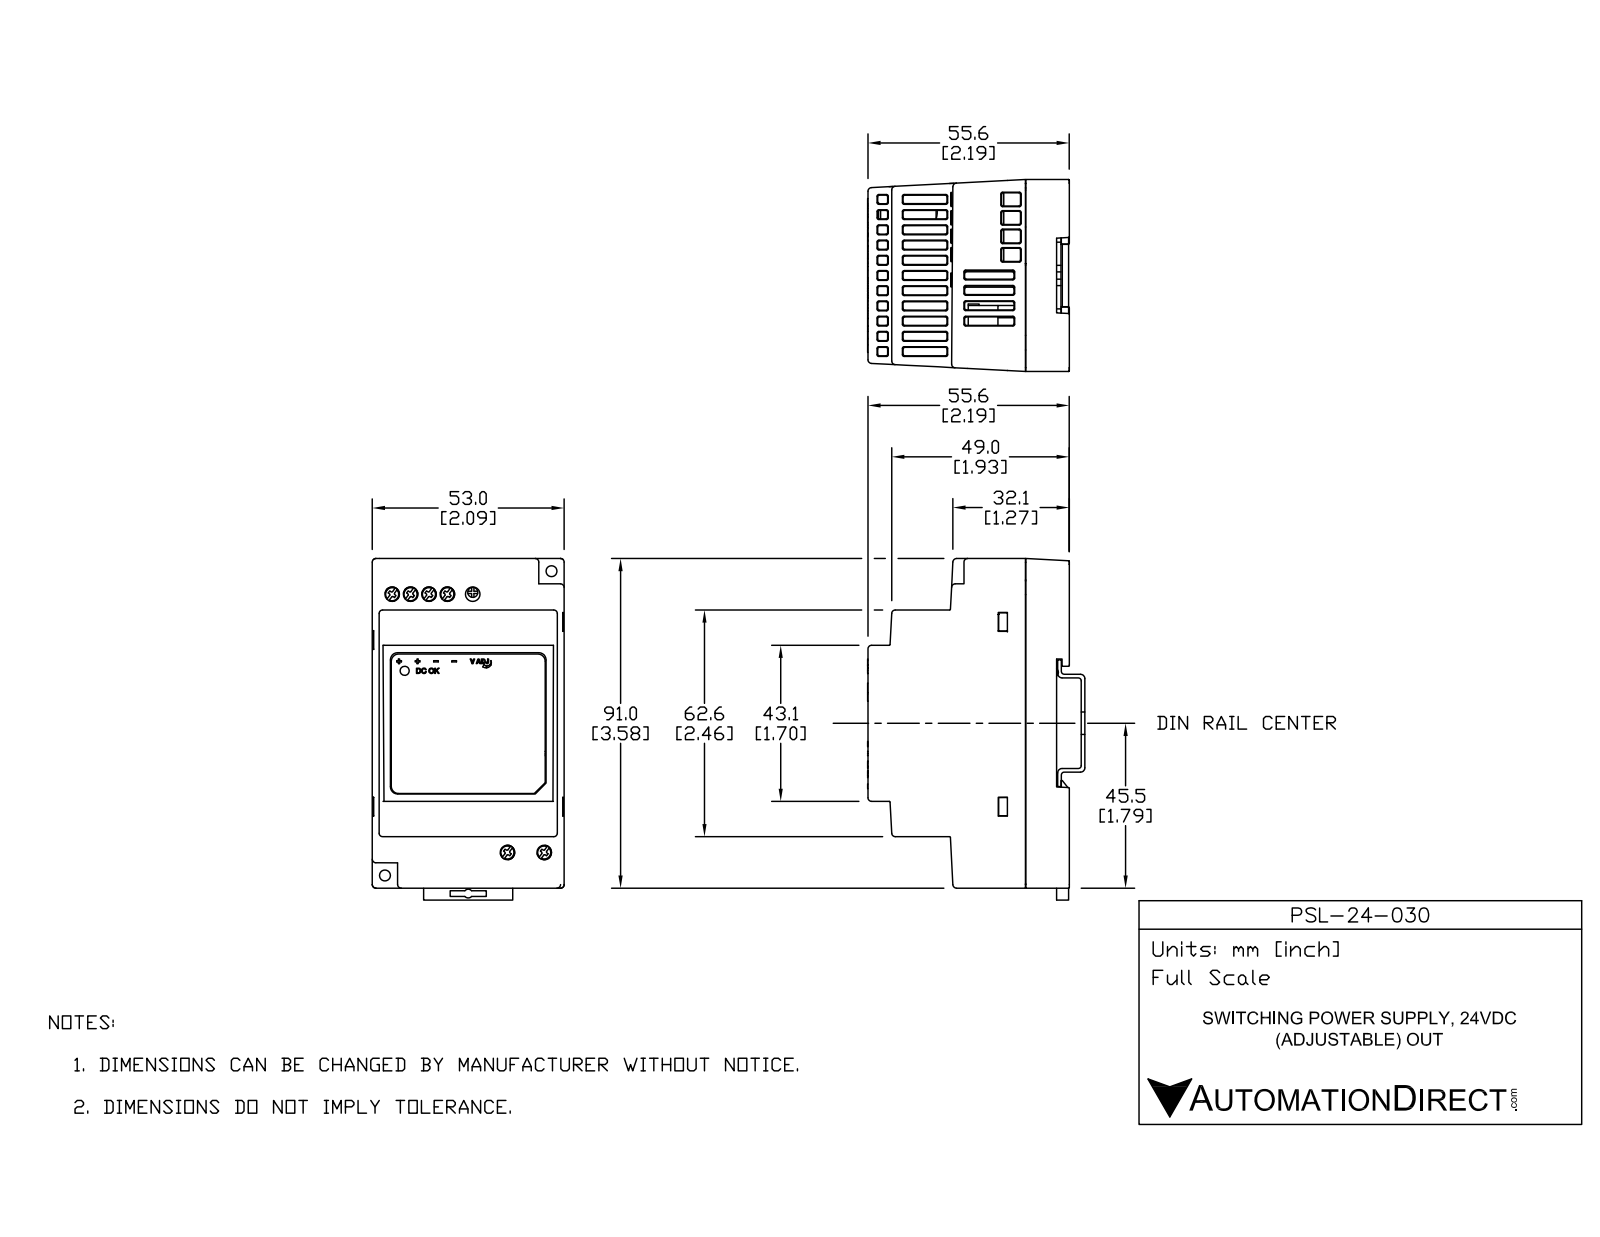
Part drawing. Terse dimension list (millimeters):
name: PSL-24-030
written by: SolidWorks 2017 (AUTOMOTIVE_DESIGN)
unit: mm
bodies: 21 solids, 2276 faces (1452 planar, 598 cylindrical, 226 other)
size: 94.3 × 55.6 × 53
volume: 53 960 mm³; area: 62 940 mm²
holes: 14× ⌀4, 4× ⌀1, 2× ⌀2.5, 2× ⌀3, 2× ⌀3.5, 2× ⌀5, 1× ⌀2.8, 1× ⌀4
bosses: 6× ⌀1.8, 3× ⌀0.5, 1× ⌀5, 1× ⌀4
rounds: 236× R0.5, 107× R0.2, 62× R1, 24× R0.3, 7× R0.2, 6× R0.5, 3× R2, 2× R0.8
face distances: 3.2, 2, 4.4, 6.4, 1.2, 5.2, 50.1, 1.8, 48.1, 44.9
hole spacings: 5.1, 75.4, 3.1, 76.1, 78.1, 10.2, 72, 5.1
